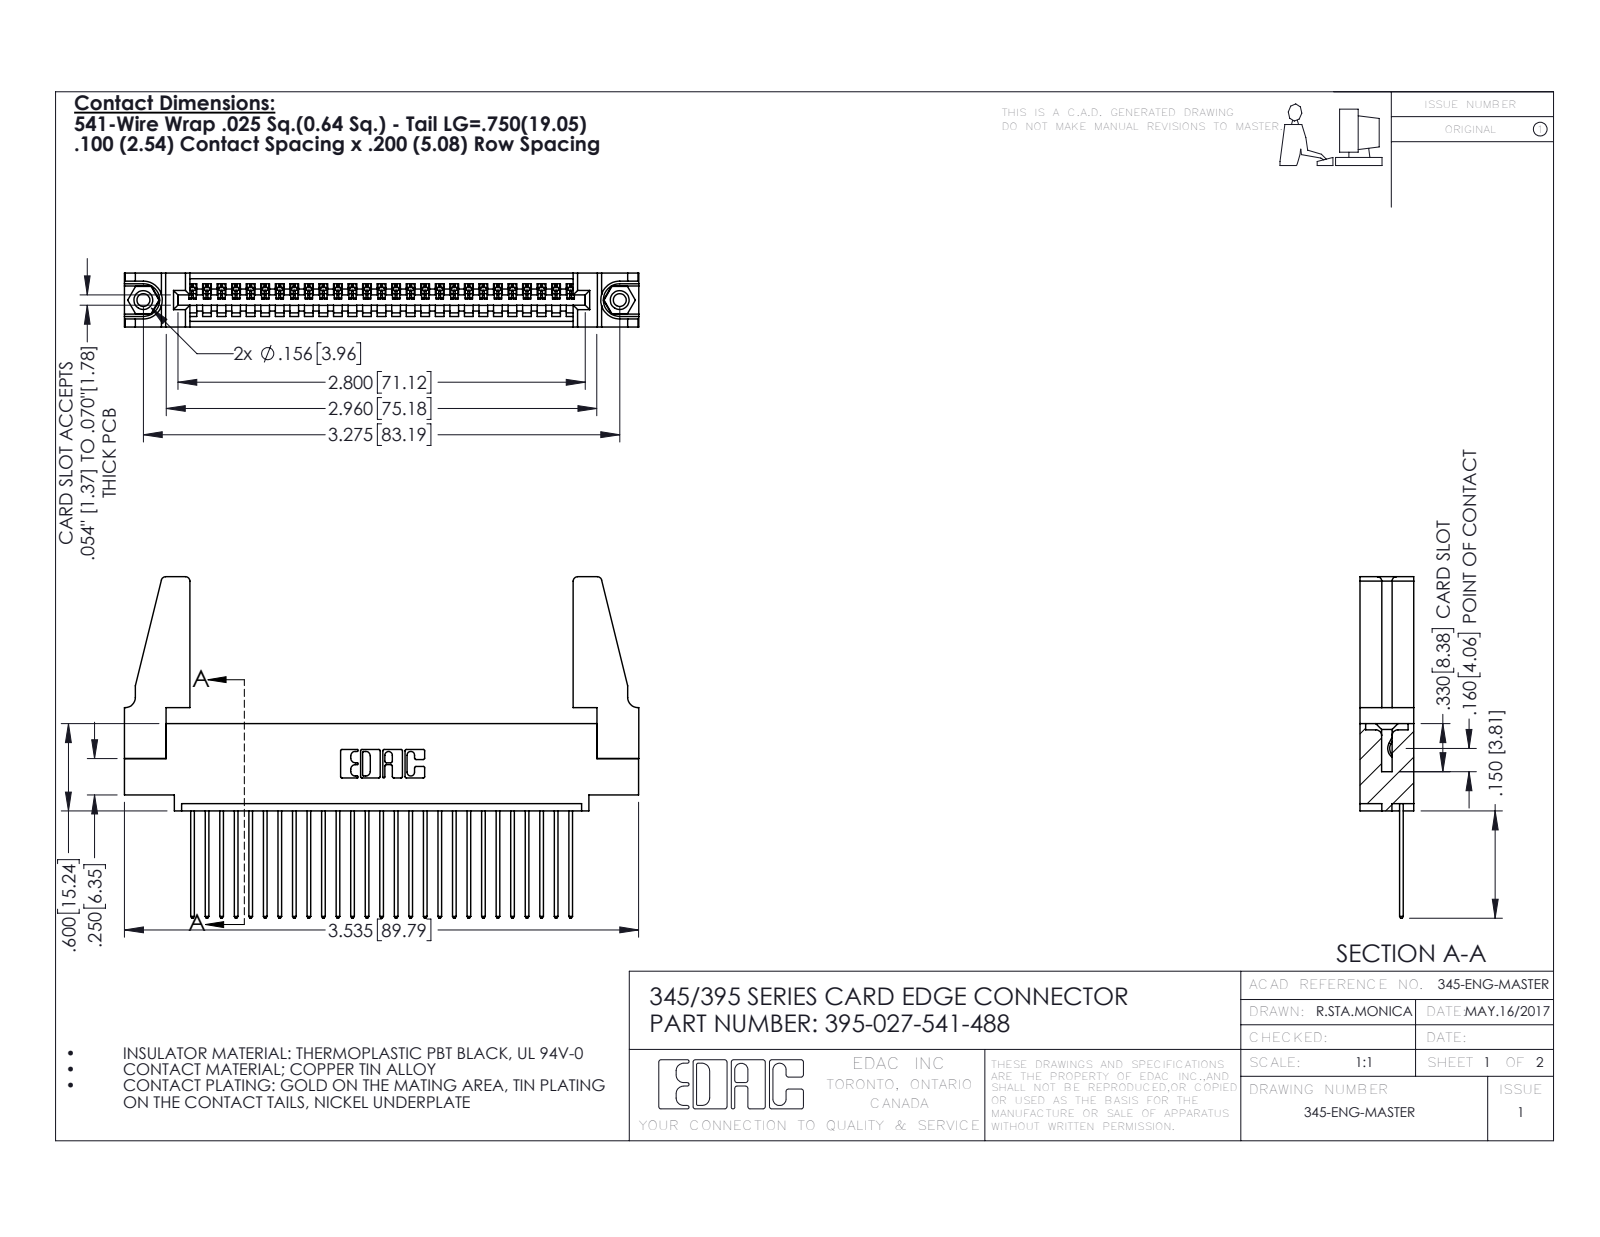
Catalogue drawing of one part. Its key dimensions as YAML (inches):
part_name: "345-220-078_345-220-088; 345-250-001_345-250-001-102; 345-292-001_345-293-141; 345 Part_0.110 Offset - 0.156 Dia-TH (+1 more)"
step_written_by: "SolidWorks 2016 (CONFIG_CONTROL_DESIGN)"
units: inches
bodies: {solids: 32, faces: 1820, planar: 1236, cylindrical: 568, other: 16}
overall_size: [3.536, 2.347, 0.37]
volume: 0.713
surface_area: 22.82
round_holes:
  - {diameter: 0.089, count: 2}
  - {diameter: 0.125, count: 2}
  - {diameter: 0.156, count: 2}
  - {diameter: 0.064, count: 1}
round_bosses_or_shafts:
  - {diameter: 0.155, count: 2}
partial_cylinders:
  - {radius: 0.006, count: 54}
  - {radius: 0.01, count: 54}
  - {radius: 0.01, count: 22}
  - {radius: 0.03, count: 8}
  - {radius: 0.007, count: 6}
  - {radius: 0.031, count: 6}
  - {radius: 0.026, count: 3}
  - {radius: 0.031, count: 2}
face_to_face_distances: [0.072, 0.298, 0.37, 0.098, 0.272, 0.025, 0.2, 0.225, 0.149, 0.072]
hole_center_spacings: [0.27, 3.04, 3.275]
